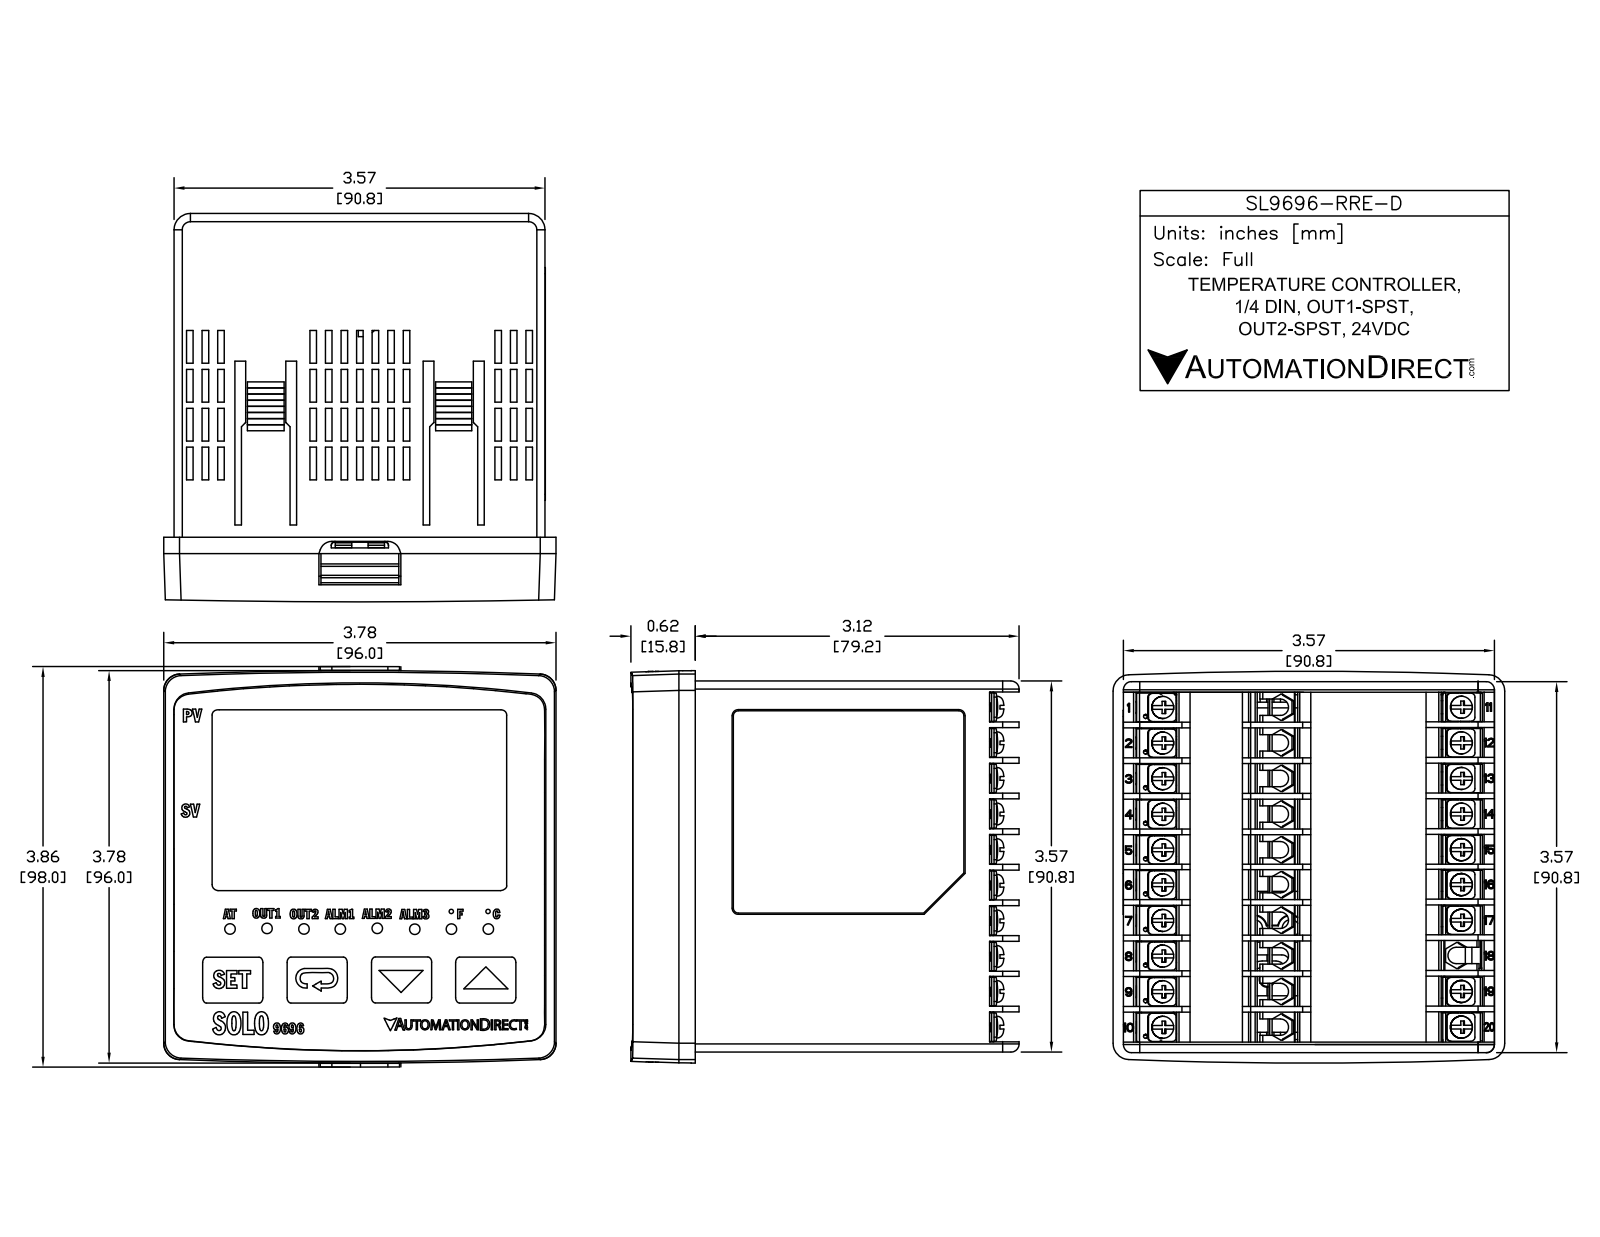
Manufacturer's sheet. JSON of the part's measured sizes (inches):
{"part_name": "SL9696-RRE-D", "step_written_by": "SolidWorks 2011 (AUTOMOTIVE_DESIGN)", "units": "inches", "bodies": {"solids": 1, "faces": 1858, "planar": 1402, "cylindrical": 248, "other": 208}, "overall_size": [3.84, 3.84, 3.751], "volume_in3": 45.14, "surface_area_in2": 106.7, "round_holes": [[0.247, 10]], "round_bosses_or_shafts": [[0.229, 20]], "partial_cylinders_radius": [[0.03, 80], [0.06, 18], [0.1, 8], [0.125, 8], [0.12, 3], [0.055, 2], [0.085, 2], [45.3, 2]], "face_to_face_distances": [3.57, 3.393, 3.392, 0.105, 3.675, 3.569, 0.343, 0.06, 3.51, 1.372], "hole_center_spacings": [1.026, 0.342, 0.684, 1.368, 1.71, 2.052, 0.342, 0.684]}
